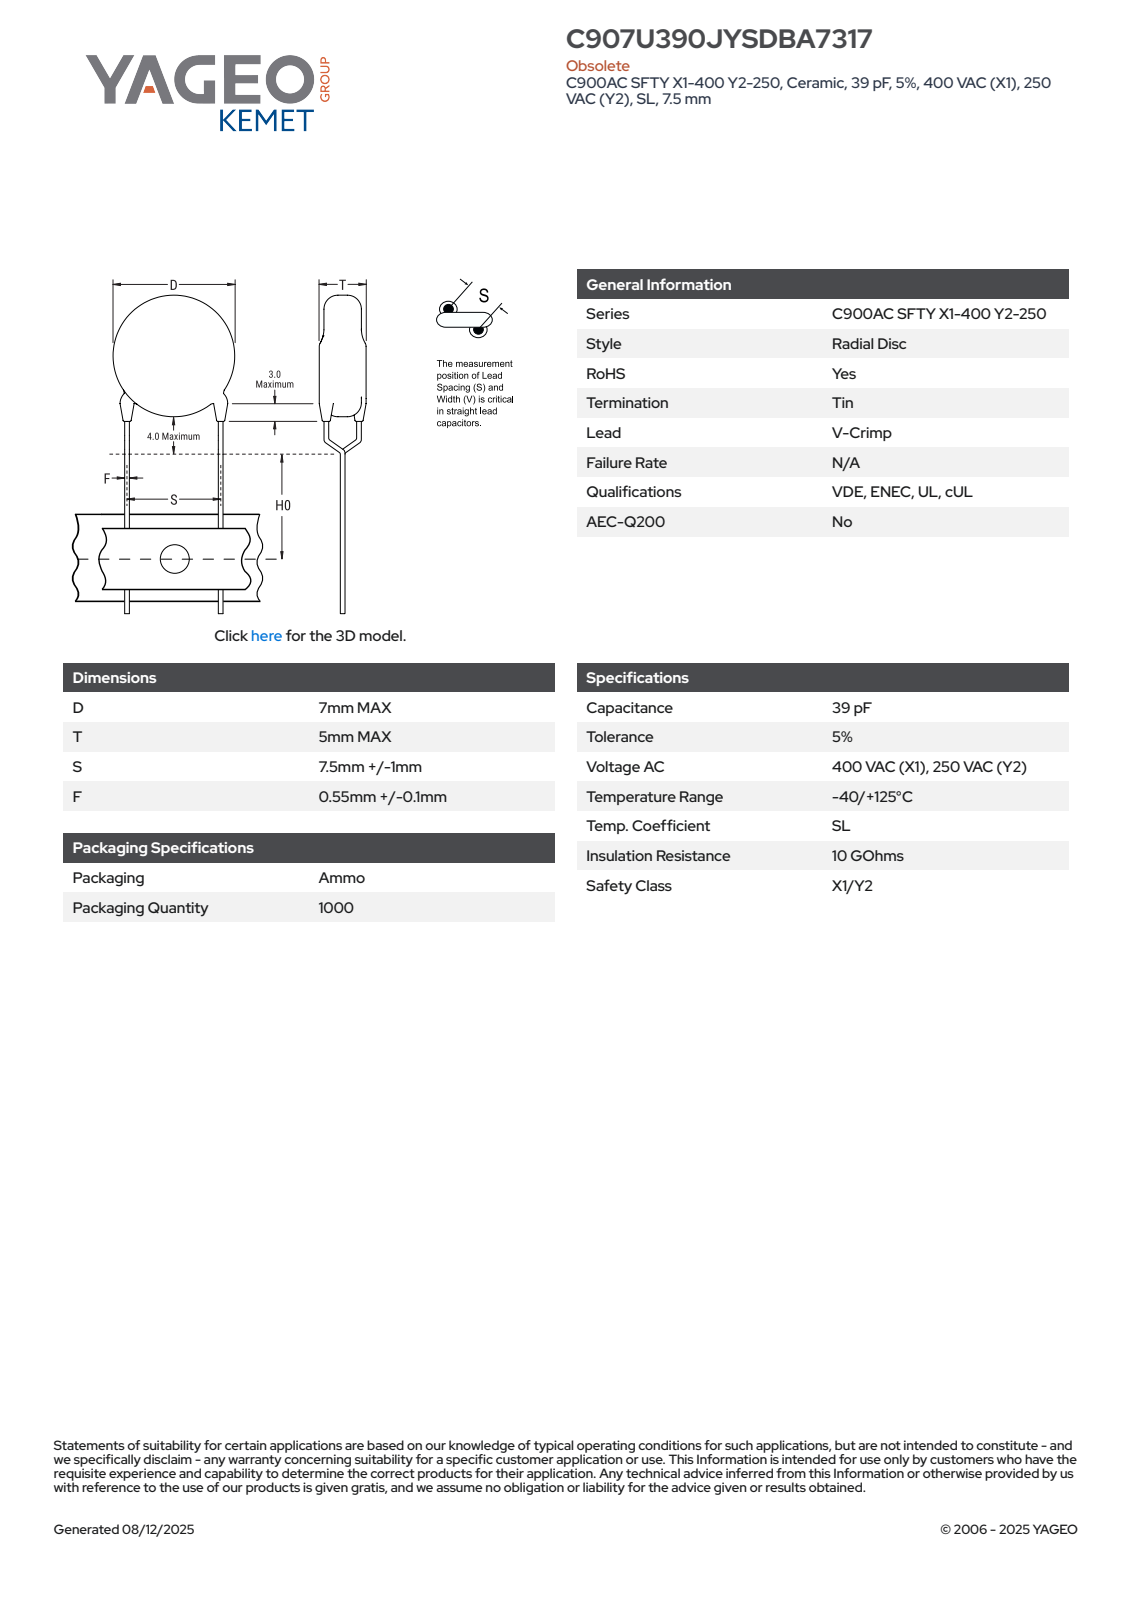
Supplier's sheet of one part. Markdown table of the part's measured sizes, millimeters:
| quantity | value |
| --- | --- |
| part name | CCD_VCC900_D7T5S7.5LL20F0.65 |
| STEP written by | SolidWorks 2014 (AUTOMOTIVE_DESIGN) |
| units | millimeters |
| bodies | 5 solids, 93 faces (65 planar, 16 cylindrical, 12 other) |
| overall size | 30.8 × 8.15 × 5 |
| volume | 203 mm³ |
| surface area | 282 mm² |
| round bosses / shafts (diameter × count) | 0.65 × 6, 7 × 1 |
| main face-to-face distances | 5, 22.9, 0.91, 27.75, 4.85, 26.84, 3.94, 3.71, 0.34, 1.87 |
